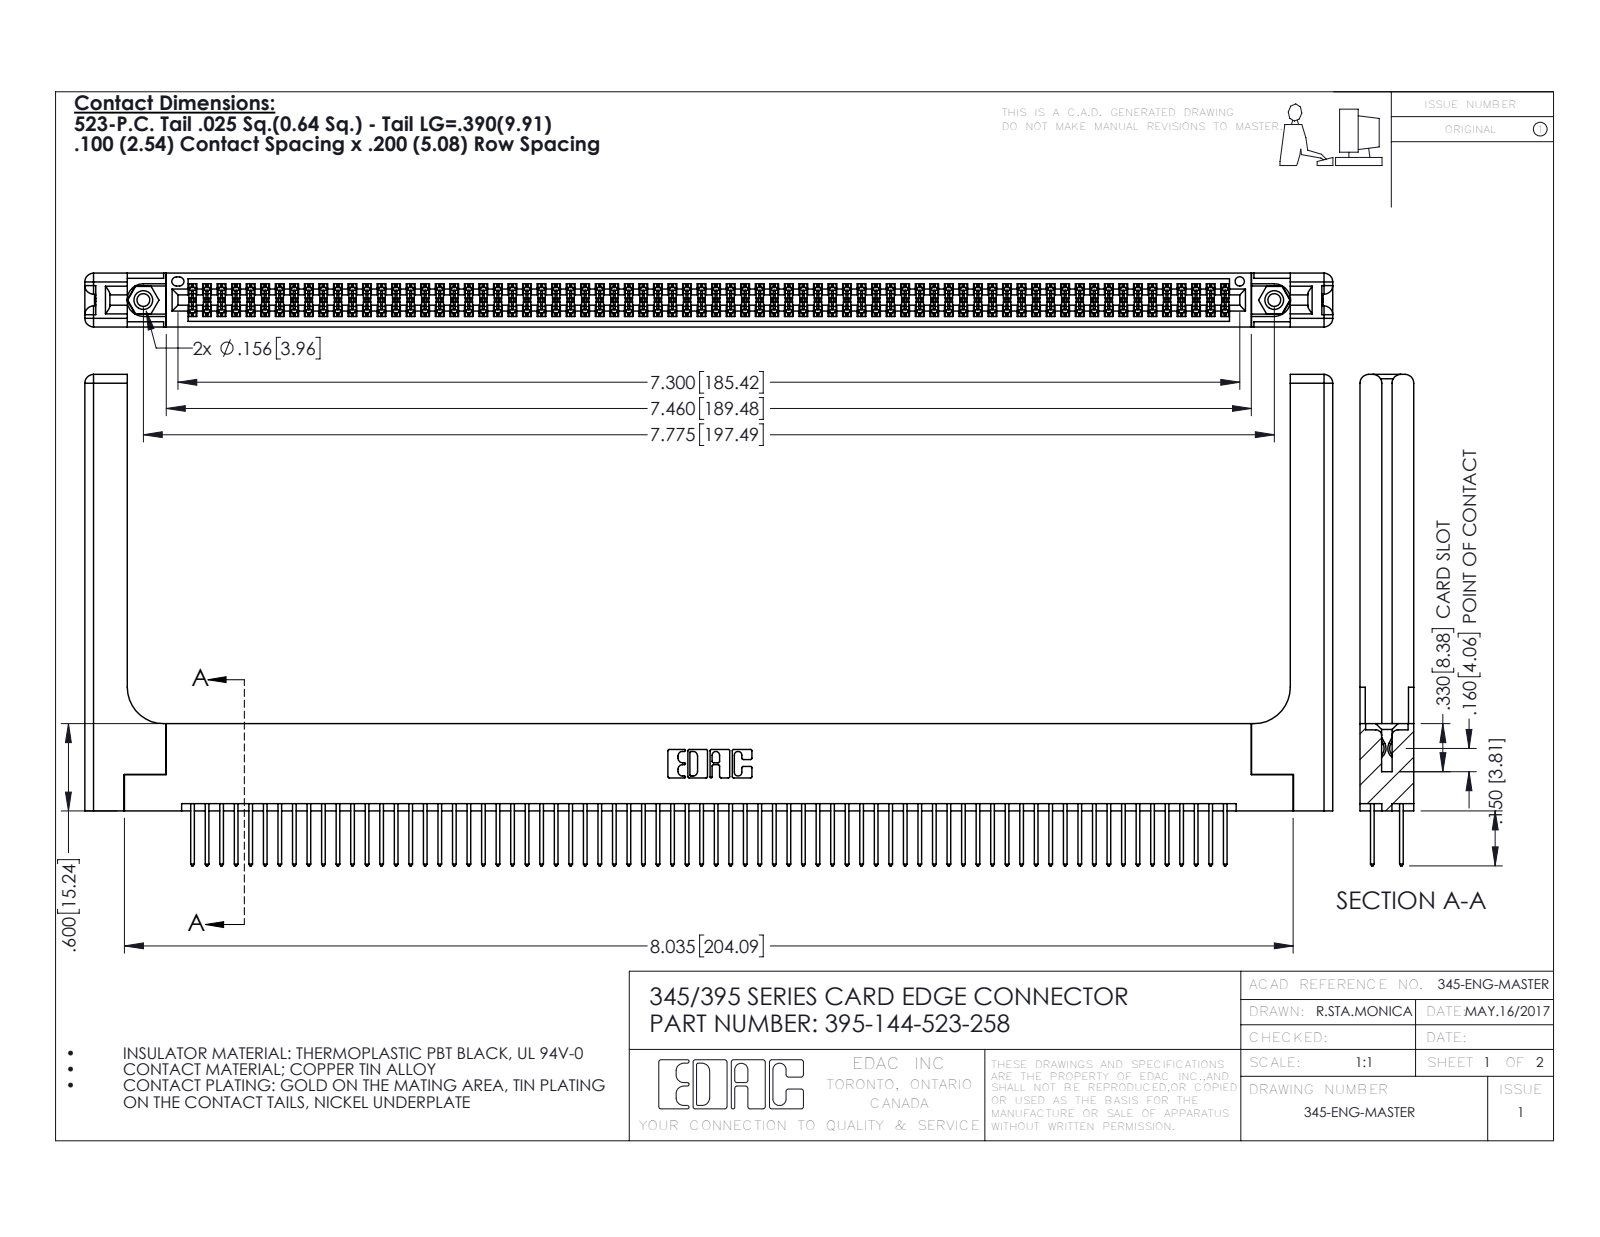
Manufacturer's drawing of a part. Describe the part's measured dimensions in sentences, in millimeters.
The part is named "345-250-001_345-250-001-102; 345-220-058_345-220-058; 395-144-523-258; 345 Part_Flush Mounting Lugs - 0.156 Dia-TH (+1 more)". Its 3-D file was written by "SolidWorks 2016 (CONFIG_CONTROL_DESIGN)". It is 149 solids with 7582 faces: 4980 planar, 2542 cylindrical and 60 other. Overall it measures 217.9 by 85.8 by 9.4 millimeters. Its volume is 30 220 cubic millimeters and its surface area 39 100 square millimeters. Round holes: 2 of diameter 2.3, 2 of diameter 3.2, 2 of diameter 4, 1 of diameter 1.6. Round bosses or shafts: 2 of diameter 3.9. Partial cylindrical surfaces (rounded edges, fillets, slot ends): 216 of radius 0.2, 144 of radius 0.3, 22 of radius 0.3, 16 of radius 1.5, 6 of radius 0.2, 6 of radius 0.8, 3 of radius 0.7, 2 of radius 0.4. The main face-to-face distances are 1.8, 7.6, 9.4, 5.1, 2.5, 6.9, 0.6, 5.7, 4.4, 3.8. The hole center spacings are 6.9, 191.5, 197.5.
